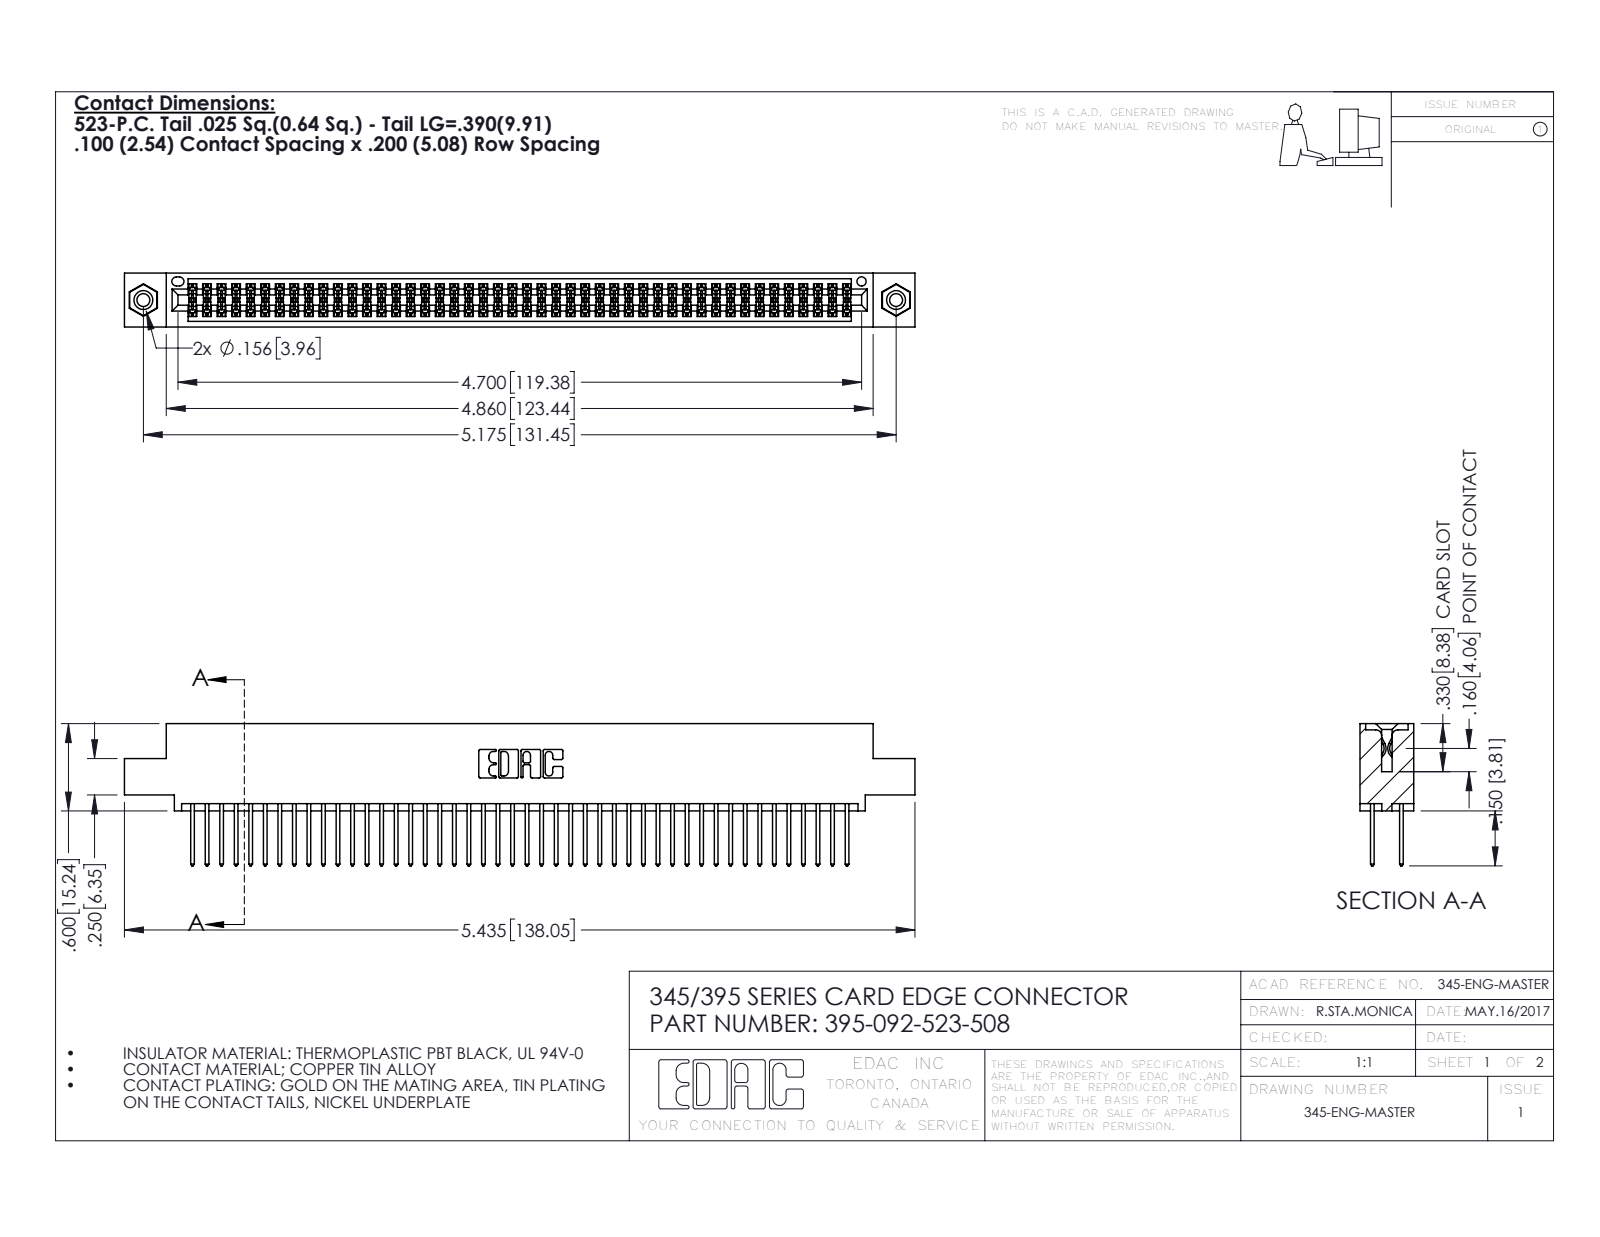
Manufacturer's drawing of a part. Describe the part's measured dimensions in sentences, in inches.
The part is named "345-292-001_345-293-123; 345-250-001_345-250-003-102; 345 Part_0.110 Offset - 0.156 Dia-TI; 395-092-523-508". Its 3-D file was written by "SolidWorks 2016 (CONFIG_CONTROL_DESIGN)". It is 95 solids with 4790 faces: 3152 planar, 1622 cylindrical and 16 other. Overall it measures 5.435 by 0.977 by 0.37 inches. Its volume is 0.827 cubic inches and its surface area 32.65 square inches. Round holes: 2 of diameter 0.089, 2 of diameter 0.125, 2 of diameter 0.156, 1 of diameter 0.064. Round bosses or shafts: 2 of diameter 0.155. Partial cylindrical surfaces (rounded edges, fillets, slot ends): 138 of radius 0.006, 92 of radius 0.01, 22 of radius 0.01, 6 of radius 0.007, 6 of radius 0.031, 3 of radius 0.026, 2 of radius 0.014, 2 of radius 0.019. The main face-to-face distances are 0.072, 0.298, 0.2, 0.098, 0.272, 0.025, 0.37, 0.225, 0.175, 0.149. The hole center spacings are 0.27, 4.939, 5.175.
